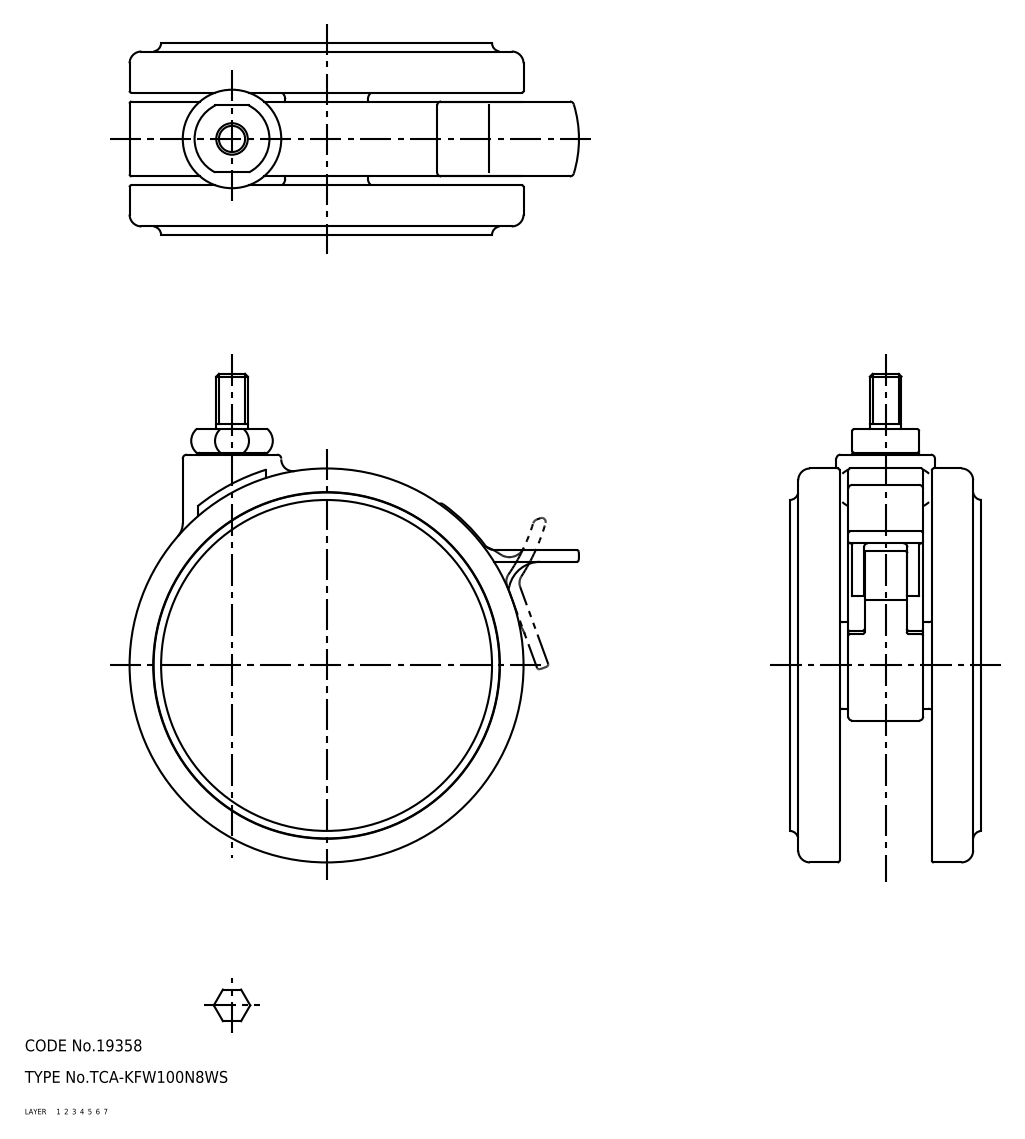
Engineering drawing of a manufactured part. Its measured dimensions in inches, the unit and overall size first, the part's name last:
Units: inches
Overall size (bounding box): 4.882 × 4.491 × 1.913
Round holes (diameter × count): ⌀0.094 ×1, ⌀0.118 ×1, ⌀0.13 ×1, ⌀0.142 ×1, ⌀0.228 ×1, ⌀0.24 ×1, ⌀0.318 ×1, ⌀0.354 ×1, ⌀0.366 ×1, ⌀0.421 ×1, ⌀0.484 ×1, ⌀0.512 ×1
Round bosses / shafts (diameter × count): ⌀0.315 ×2, ⌀3.937 ×1, ⌀3.457 ×1, ⌀0.984 ×1, ⌀0.866 ×1, ⌀0.787 ×1, ⌀0.669 ×1, ⌀0.413 ×1
Partial cylindrical surfaces — rounded edges, fillets, slot ends (radius × count): R0.02 ×63, R0.039 ×61, R0.059 ×21, R0.008 ×18, R0.012 ×17, R0.079 ×16, R0.118 ×7, R0.028 ×2
Main face-to-face distances: 0.071, 1.772, 1.843, 0.142, 1.701, 0.496, 1.276, 0.354, 1.417, 0.425
Hole centre spacings: 0.843, 1.18, 1.732
Volume: 11.27 in³ · Surface area: 148 in²
Bodies: 1 solid, 1520 faces (528 planar, 654 cylindrical, 338 other)
Part name (STEP PRODUCT): caster; TCA-KFW100N8WS
STEP written by: SolidWorks 2015 (AUTOMOTIVE_DESIGN)
